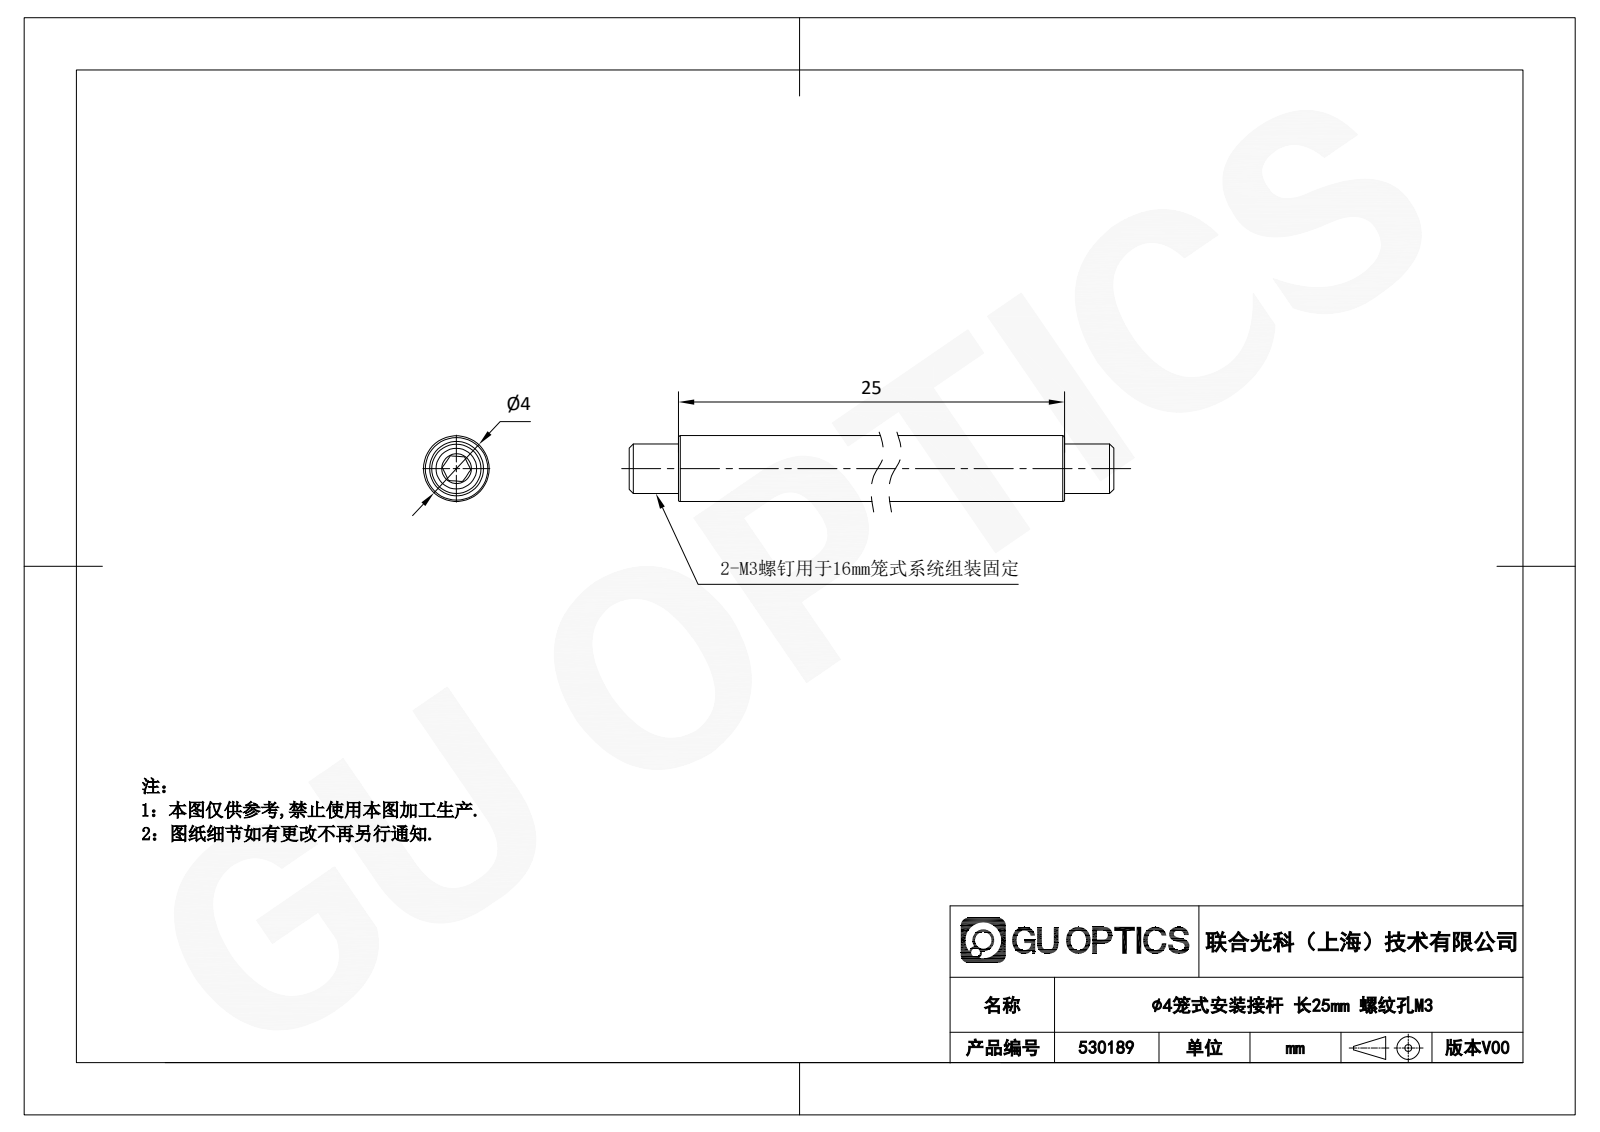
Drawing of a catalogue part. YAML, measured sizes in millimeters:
part_name: "530189"
step_written_by: "SolidWorks 2020 (CONFIG_CONTROL_DESIGN)"
units: millimeters
bodies: {solids: 3, faces: 37, planar: 20, cylindrical: 5, other: 12}
overall_size: [35, 4, 4]
volume: 364
surface_area: 604
round_holes:
  - {diameter: 2.5, count: 1}
round_bosses_or_shafts:
  - {diameter: 4, count: 1}
  - {diameter: 3, count: 1}
face_to_face_distances: [3, 22, 5, 8, 27, 30, 1.5, 25, 1, 34]
